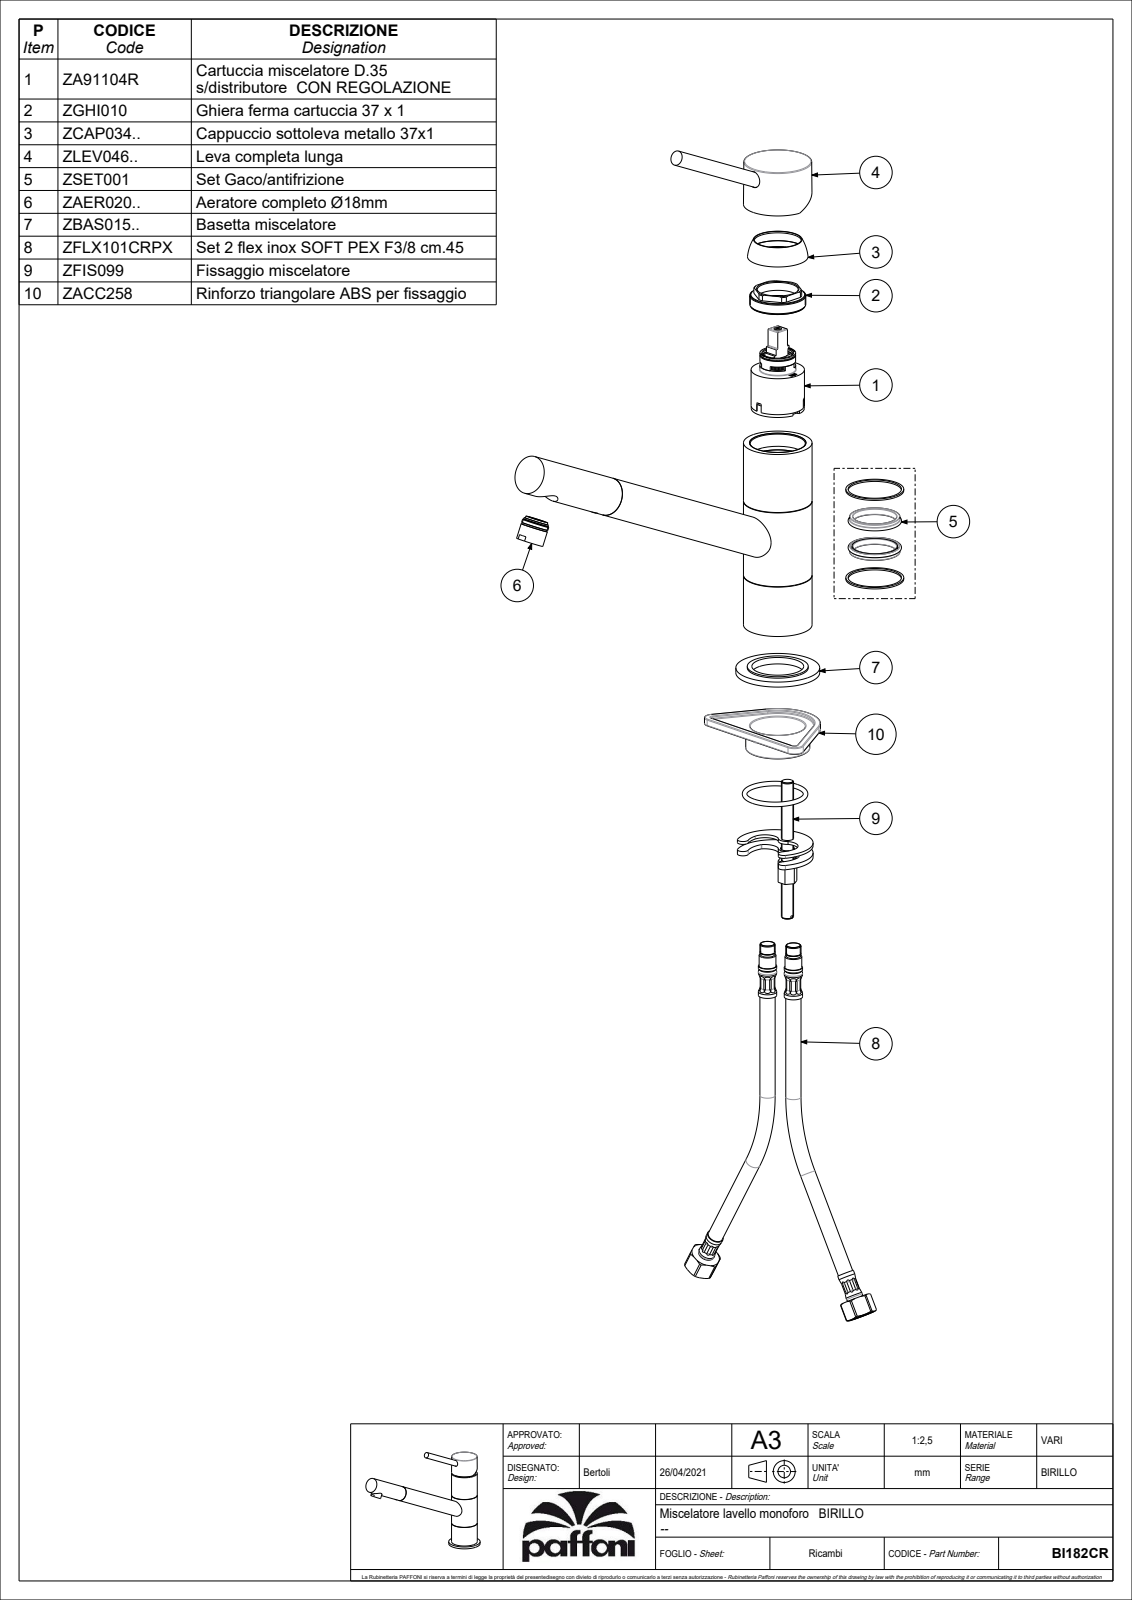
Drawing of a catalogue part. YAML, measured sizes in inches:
part_name: "BI182CR"
step_written_by: "CREO PARAMETRIC BY PTC INC, 2020044 (CONFIG_CONTROL_DESIGN)"
units: inches
bodies: {solids: 2, faces: 1229, planar: 639, cylindrical: 337, other: 253}
overall_size: [10.357, 7.596, 2.165]
volume: 13.78
surface_area: 179
round_holes:
  - {diameter: 0.354, count: 6}
  - {diameter: 0.315, count: 3}
  - {diameter: 0.433, count: 3}
  - {diameter: 0.157, count: 2}
  - {diameter: 0.724, count: 2}
  - {diameter: 0.13, count: 1}
  - {diameter: 0.177, count: 1}
  - {diameter: 0.197, count: 1}
  - {diameter: 0.217, count: 1}
  - {diameter: 0.268, count: 1}
  - {diameter: 0.295, count: 1}
  - {diameter: 0.394, count: 1}
round_bosses_or_shafts:
  - {diameter: 0.984, count: 2}
  - {diameter: 0.551, count: 2}
  - {diameter: 2.165, count: 1}
  - {diameter: 1.772, count: 1}
  - {diameter: 1.575, count: 1}
  - {diameter: 1.378, count: 1}
  - {diameter: 1.37, count: 1}
  - {diameter: 1.268, count: 1}
partial_cylinders:
  - {radius: 0.02, count: 51}
  - {radius: 0.006, count: 11}
  - {radius: 0.012, count: 4}
  - {radius: 0.039, count: 2}
  - {radius: 0.041, count: 1}
  - {radius: 0.197, count: 1}
  - {radius: 0.276, count: 1}
  - {radius: 0.366, count: 1}
face_to_face_distances: [2.039, 0.138, 4.11, 3.972, 4.787, 0.039, 0.374, 0.575, 2.488, 0.563]
hole_center_spacings: [0.098, 0.293, 0.339, 0.397, 0.472, 0.53, 0.551, 0.56]
